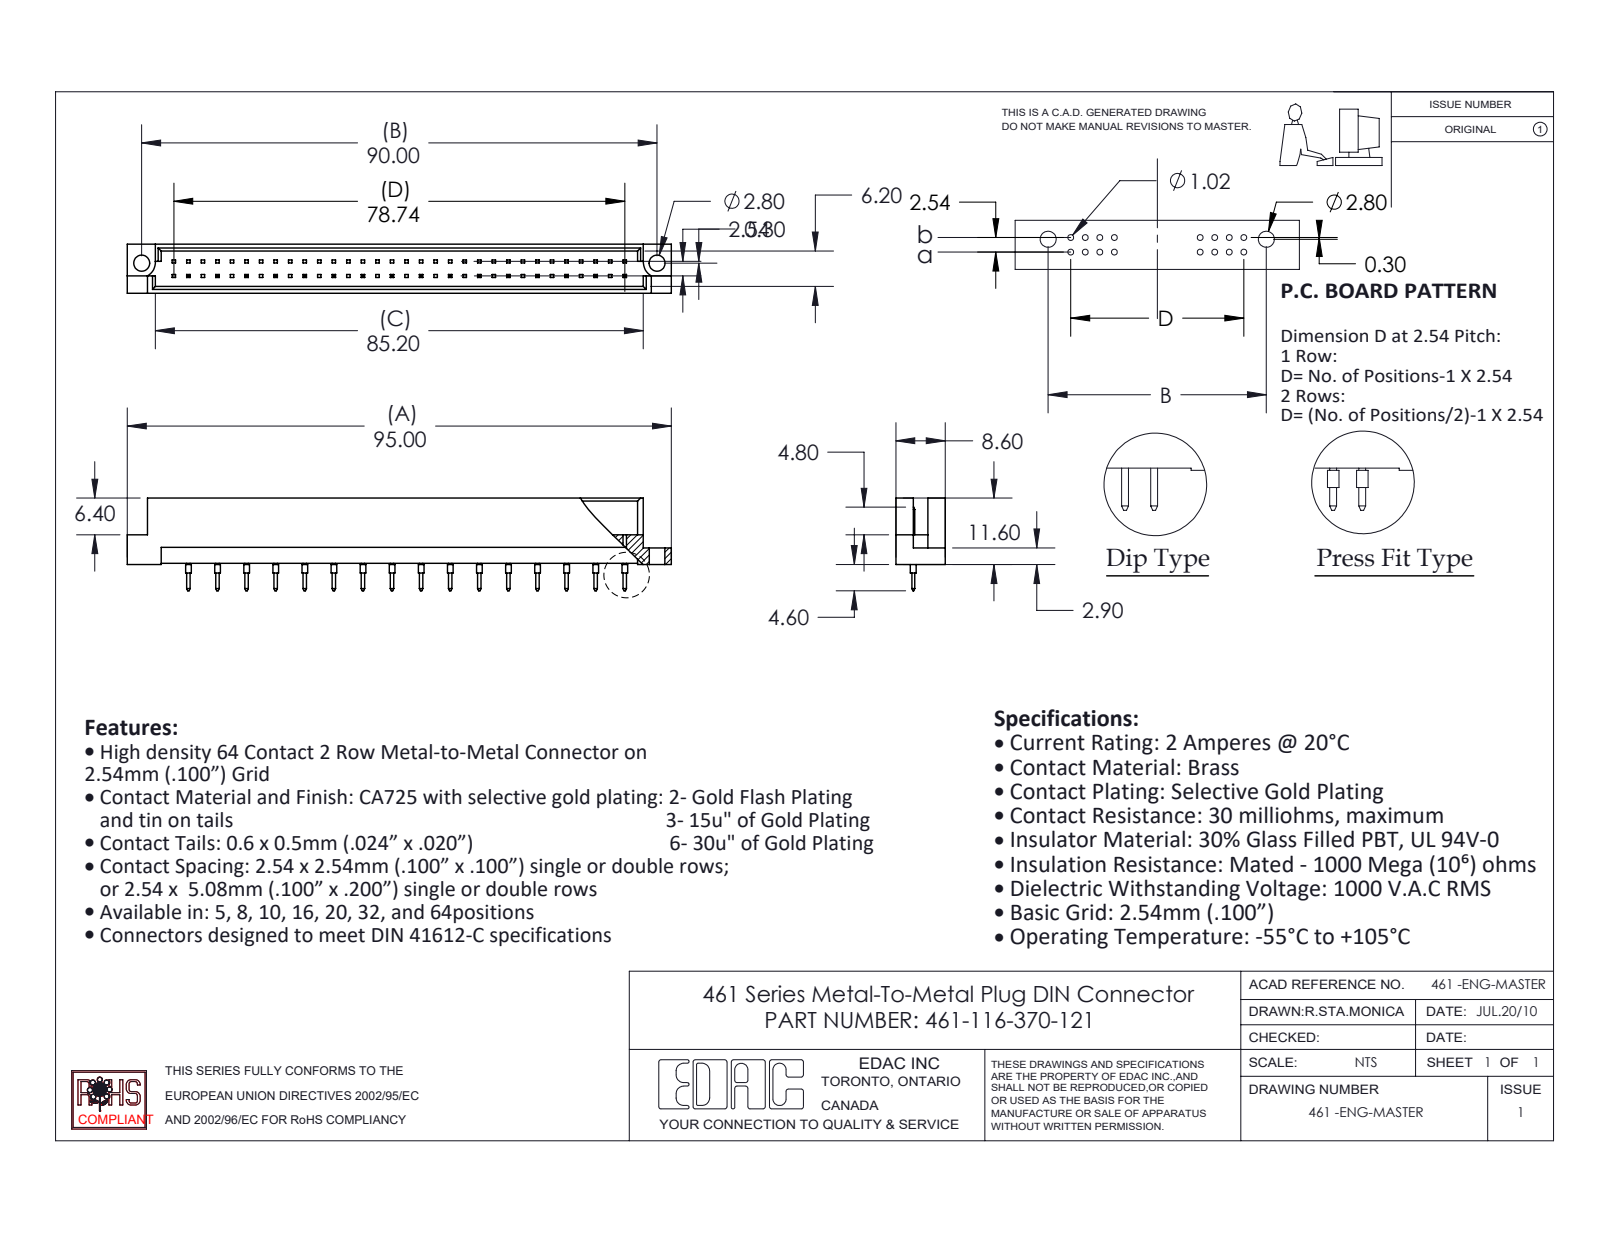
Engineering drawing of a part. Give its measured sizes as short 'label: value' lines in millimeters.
name: 461-290_70; 461-116-370-221; 461 Part_64
written by: SolidWorks 2020 (CONFIG_CONTROL_DESIGN)
unit: mm
bodies: 17 solids, 657 faces (618 planar, 39 cylindrical, 0 other)
size: 95 × 16.2 × 8.6
volume: 4 737 mm³; area: 6 218 mm²
holes: 2× ⌀2.8
bosses: 16× ⌀1
rounds: 2× R2.8
face distances: 1.2, 7.4, 8.6, 6.2, 5, 1.58, 3.28, 5.32, 2.08, 4.12
hole spacings: 90
